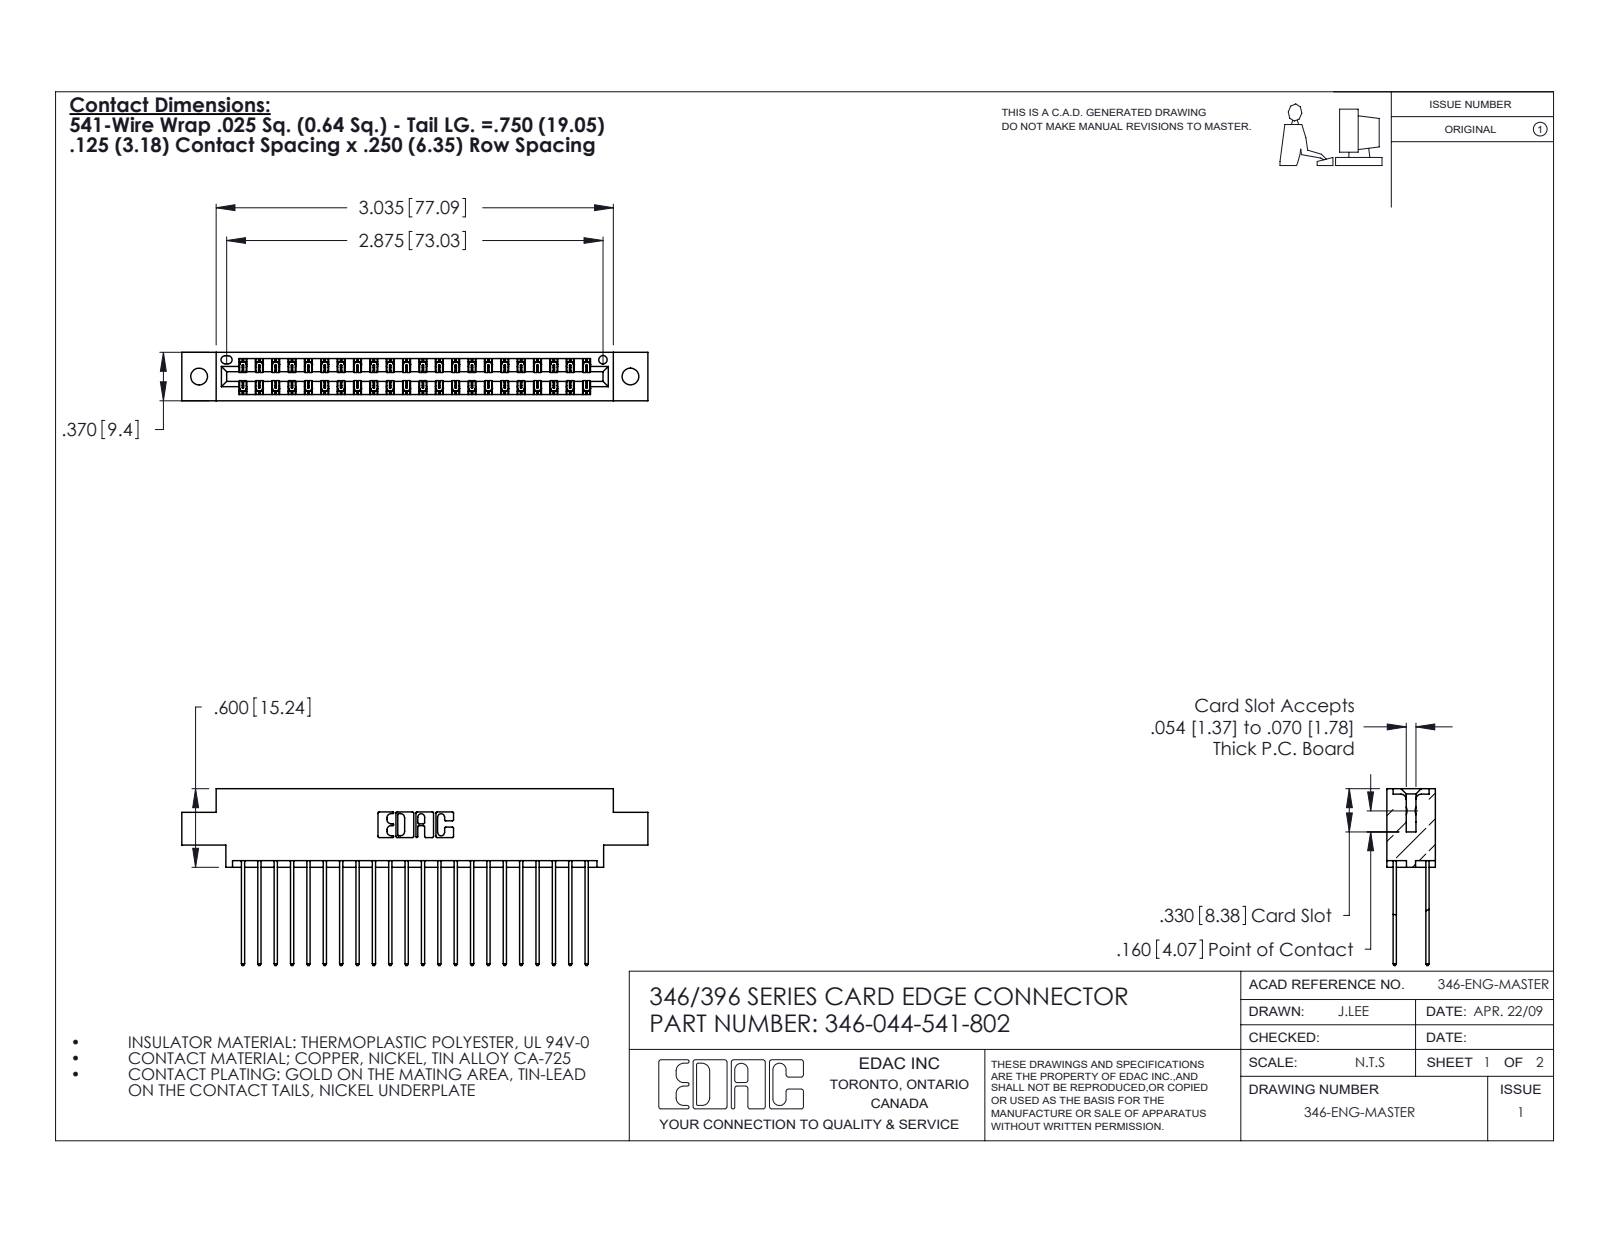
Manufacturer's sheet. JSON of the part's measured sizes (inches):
{"part_name": "346-044-541-802; 345-292-001_345-293-141; 346 Part_0.170 Offset - 0.128 Dia", "step_written_by": "SolidWorks 2020 (CONFIG_CONTROL_DESIGN)", "units": "inches", "bodies": {"solids": 45, "faces": 2414, "planar": 1620, "cylindrical": 794, "other": 0}, "overall_size": [3.56, 1.35, 0.37], "volume_in3": 0.532, "surface_area_in2": 19.84, "round_holes": [[0.128, 2], [0.064, 1]], "partial_cylinders_radius": [[0.006, 66], [0.01, 44], [0.01, 22], [0.007, 6], [0.031, 6], [0.026, 3], [0.014, 2], [0.022, 2]], "face_to_face_distances": [0.048, 0.322, 0.25, 0.072, 0.298, 0.025, 0.37, 0.275, 0.225, 0.148], "hole_center_spacings": [0.246, 3.087, 3.295]}
